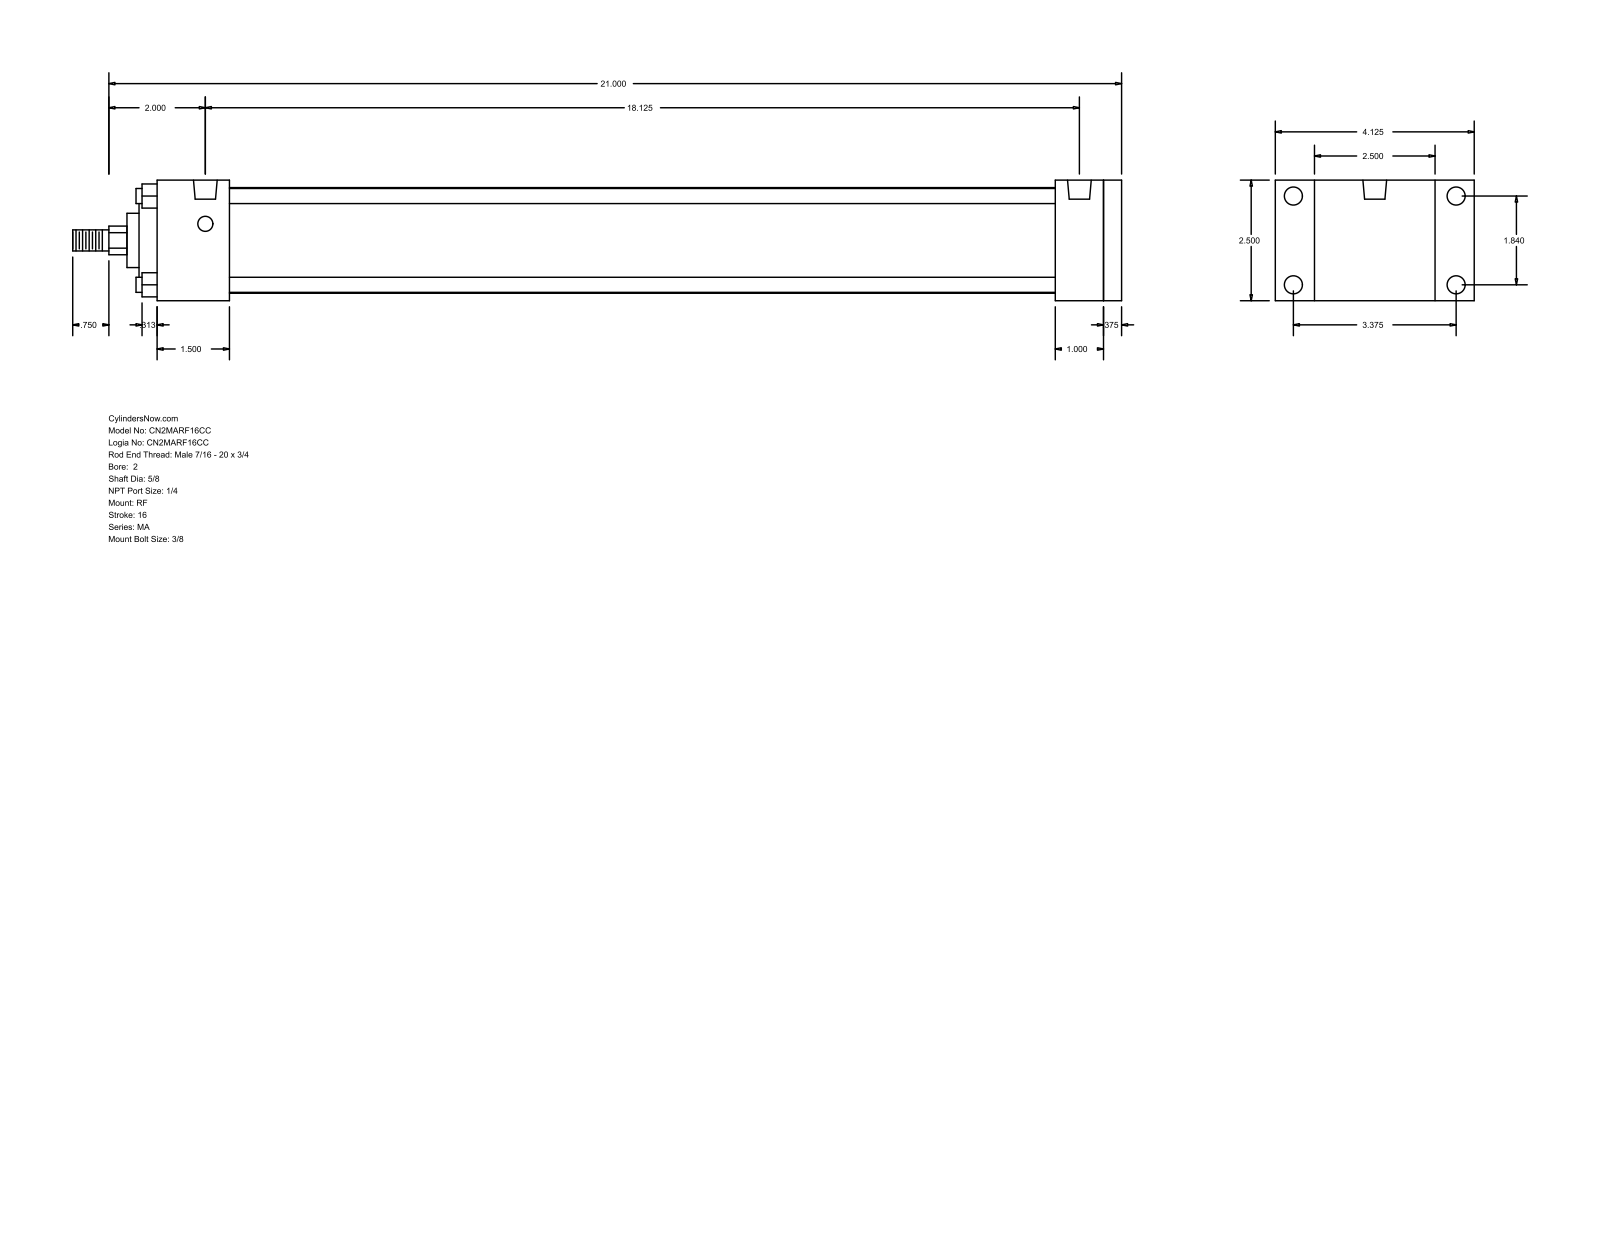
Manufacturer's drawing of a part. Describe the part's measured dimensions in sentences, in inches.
The part is named "MA_RF__0200_0.625". Its 3-D file was written by "GSSL Pune (CONFIG_CONTROL_DESIGN)". It is 0 solids with 94 faces: 65 planar, 29 cylindrical and 0 other. Overall it measures 21.75 by 4.125 by 2.5 inches. Round holes: 4 of diameter 0.313, 4 of diameter 0.375, 2 of diameter 0.492. Round bosses or shafts: 4 of diameter 0.313, 1 of diameter 2.19, 1 of diameter 2, 1 of diameter 1.125, 1 of diameter 0.625, 1 of diameter 0.437. Partial cylindrical surfaces (rounded edges, fillets, slot ends): 1 of radius 0.297. The main face-to-face distances are 2.5, 0.375, 20, 1, 1.5, 19.625, 18.125, 18.5, 18.625, 17.125. The hole center spacings are 1.84, 3.375, 3.844, 18.125.
